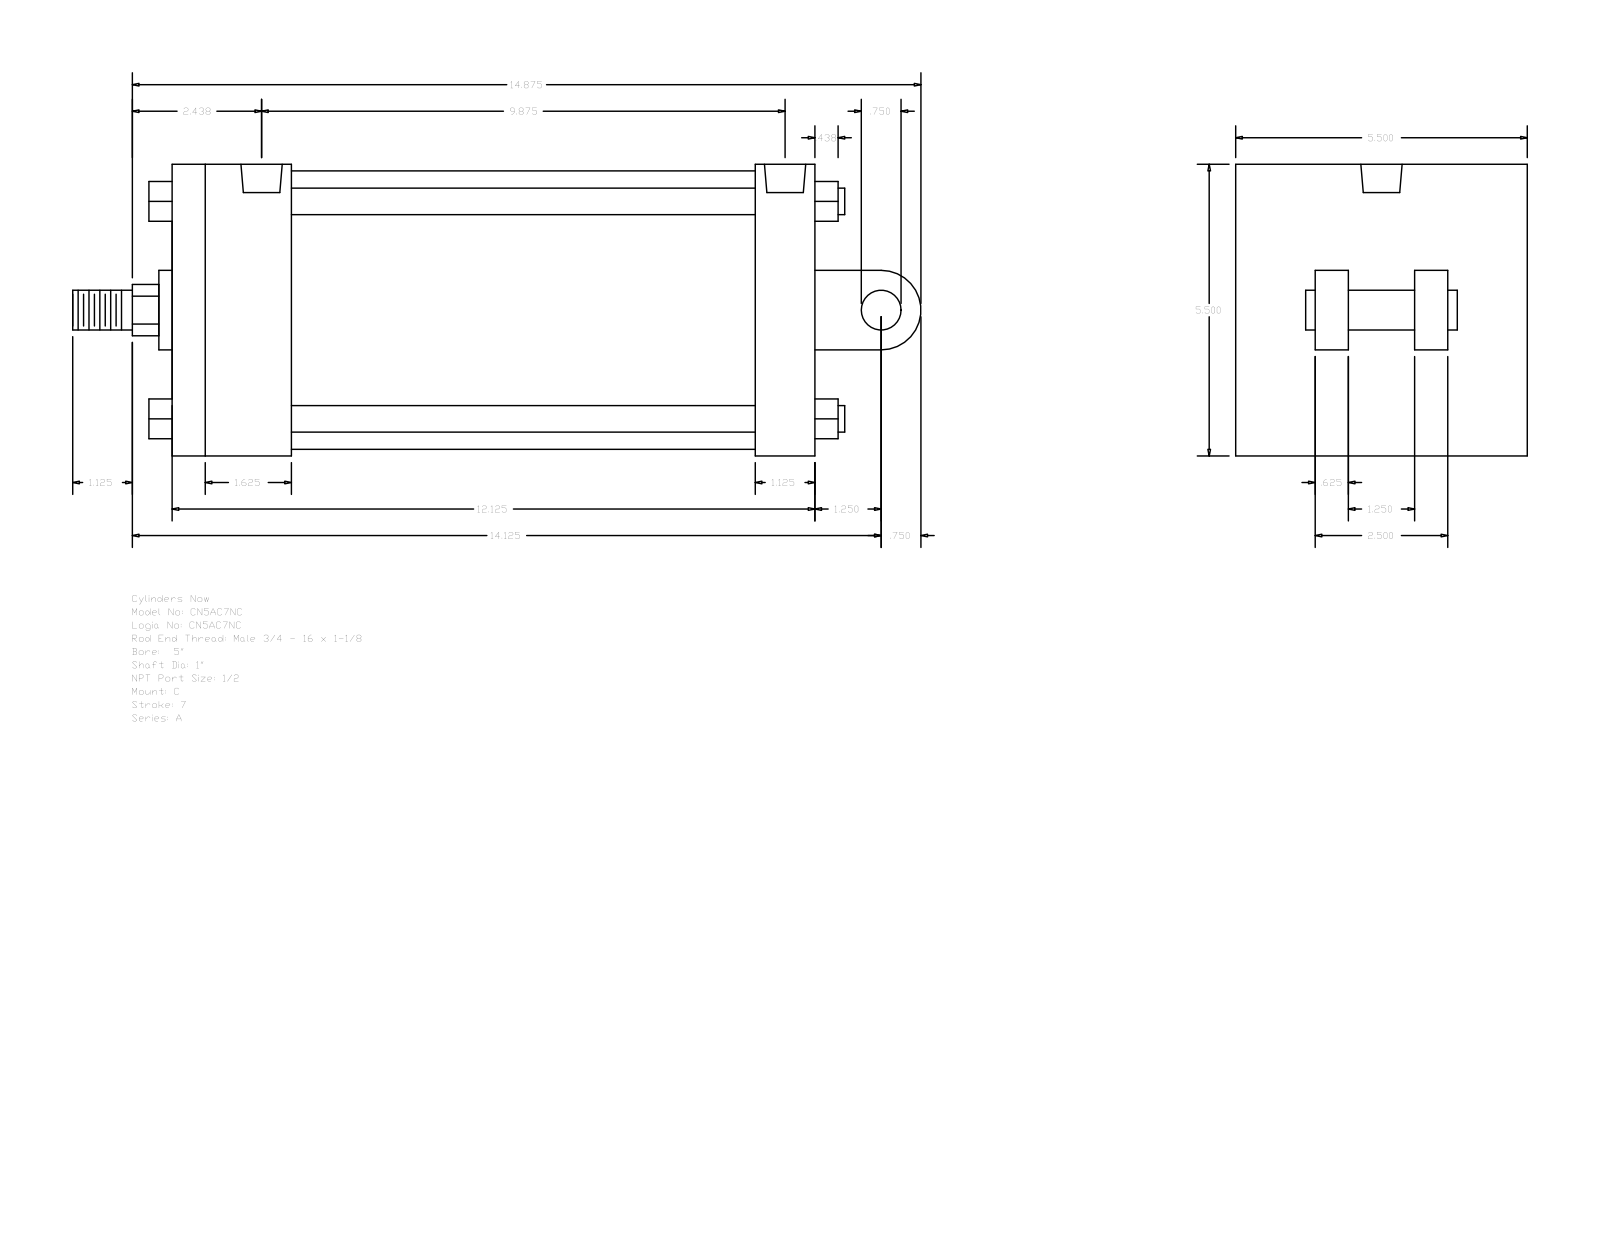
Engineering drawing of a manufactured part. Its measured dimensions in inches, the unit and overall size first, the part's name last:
Units: inches
Overall size (bounding box): 16 × 5.5 × 5.5
Round holes (diameter × count): ⌀0.344 ×4, ⌀0.778 ×2
Round bosses / shafts (diameter × count): ⌀0.5 ×4, ⌀0.75 ×2, ⌀5.25 ×1, ⌀1.5 ×1, ⌀1 ×1
Partial cylindrical surfaces — rounded edges, fillets, slot ends (radius × count): R0.484 ×1, R0.75 ×1
Main face-to-face distances: 5.5, 12.125, 1.125, 2.25, 11, 8.75, 9.875, 1.5, 4, 2.125
Hole centre spacings: 0.094, 9.687, 9.781, 9.875
Bodies: 0 solids, 135 faces (102 planar, 33 cylindrical, 0 other)
Part name (STEP PRODUCT): A_C__0500_1
STEP written by: GSSL Pune (CONFIG_CONTROL_DESIGN)
